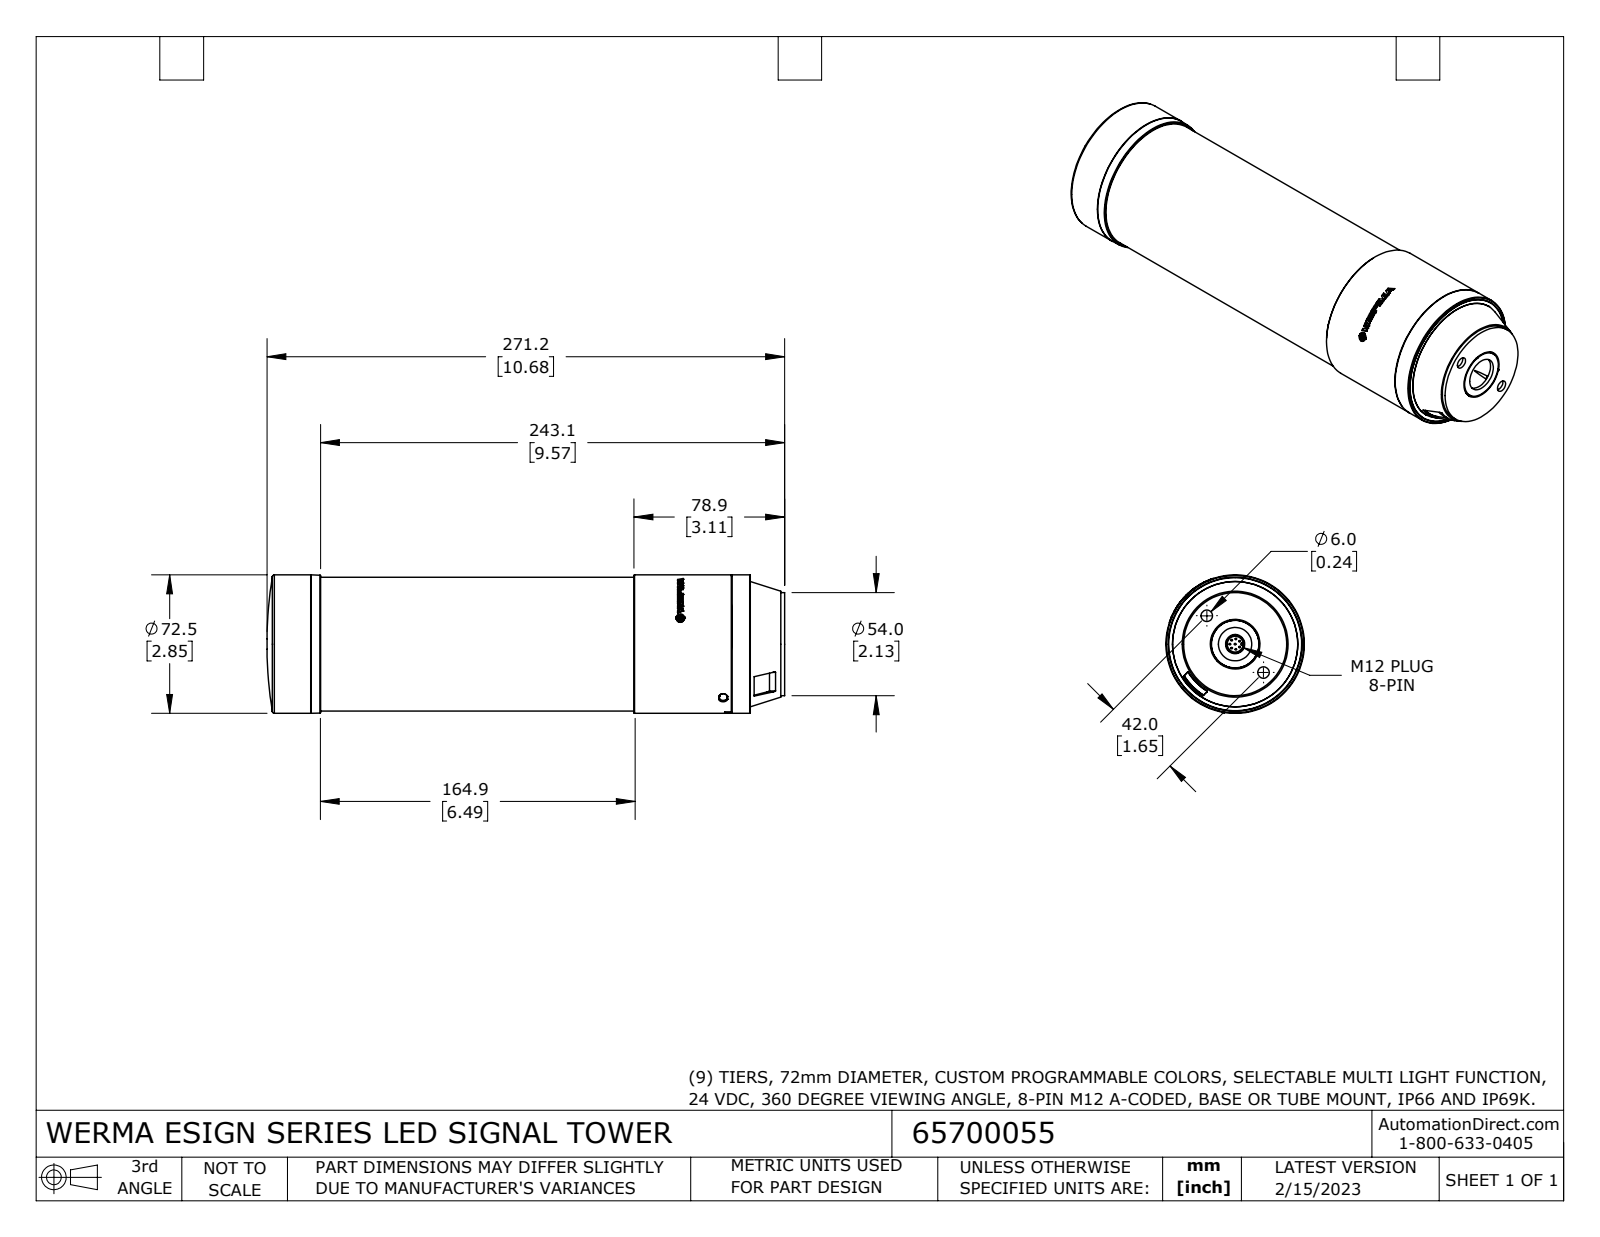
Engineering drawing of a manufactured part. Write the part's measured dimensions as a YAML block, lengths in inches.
part_name: "65700055"
step_written_by: "SolidWorks 2021 (CONFIG_CONTROL_DESIGN)"
units: inches
bodies: {solids: 1, faces: 270, planar: 107, cylindrical: 102, other: 61}
overall_size: [10.677, 2.854, 2.854]
volume: 62.91
surface_area: 110.2
round_holes:
  - {diameter: 0.236, count: 2}
  - {diameter: 0.327, count: 1}
  - {diameter: 0.396, count: 1}
  - {diameter: 0.689, count: 1}
  - {diameter: 1.024, count: 1}
round_bosses_or_shafts:
  - {diameter: 0.031, count: 8}
  - {diameter: 2.854, count: 1}
  - {diameter: 2.811, count: 1}
  - {diameter: 2.756, count: 1}
  - {diameter: 2.126, count: 1}
  - {diameter: 0.98, count: 1}
  - {diameter: 0.173, count: 1}
partial_cylinders:
  - {radius: 0.01, count: 12}
  - {radius: 0.079, count: 2}
  - {radius: 0.08, count: 2}
  - {radius: 0.099, count: 2}
  - {radius: 0.009, count: 1}
  - {radius: 0.011, count: 1}
  - {radius: 0.016, count: 1}
  - {radius: 0.024, count: 1}
face_to_face_distances: [0.079, 0.712, 0.633, 0.63, 0.709, 9.776, 9.697, 9.067, 9.063, 9.768]
hole_center_spacings: [0.827, 1.654]
